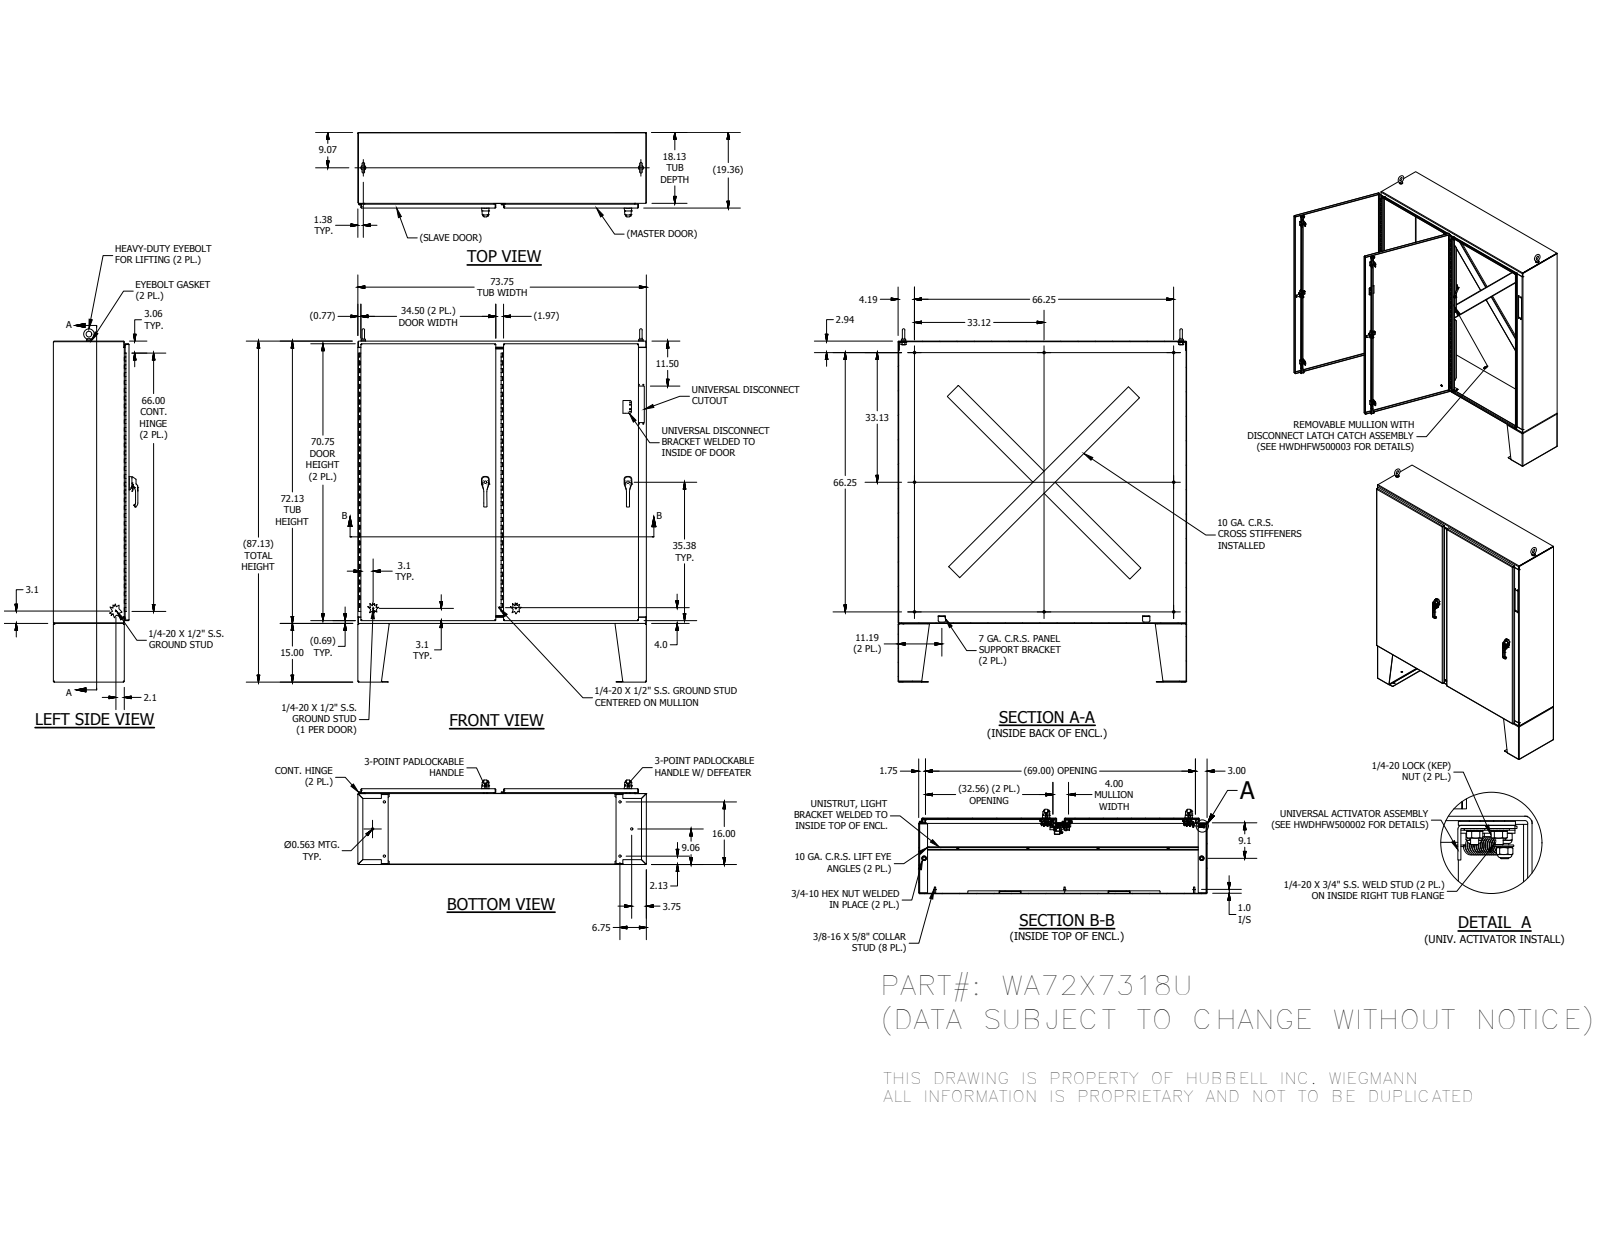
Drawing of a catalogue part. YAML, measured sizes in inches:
part_name: "WA72X7318UBLS; WAX7318UTOP; WAX7318UBTM; HFW332010S (+8 more)"
step_written_by: "Autodesk Inventor 2016 (AUTOMOTIVE_DESIGN)"
units: inches
bodies: {solids: 216, faces: 8897, planar: 4142, cylindrical: 2994, other: 1761}
overall_size: [90.248, 73.75, 21.608]
volume: 2680
surface_area: 41510
round_holes:
  - {diameter: 0.25, count: 18}
  - {diameter: 0.375, count: 18}
  - {diameter: 0.563, count: 18}
  - {diameter: 0.19, count: 8}
  - {diameter: 0.2, count: 8}
  - {diameter: 0.203, count: 8}
  - {diameter: 0.276, count: 8}
  - {diameter: 0.289, count: 8}
  - {diameter: 0.313, count: 8}
  - {diameter: 0.335, count: 8}
  - {diameter: 0.38, count: 8}
  - {diameter: 0.201, count: 7}
round_bosses_or_shafts:
  - {diameter: 0.25, count: 22}
  - {diameter: 0.33, count: 18}
  - {diameter: 0.625, count: 13}
  - {diameter: 0.337, count: 12}
  - {diameter: 0.375, count: 11}
  - {diameter: 0.563, count: 9}
  - {diameter: 1, count: 8}
  - {diameter: 0.438, count: 8}
partial_cylinders:
  - {radius: 0.02, count: 335}
  - {radius: 0.012, count: 203}
  - {radius: 0.02, count: 192}
  - {radius: 0.019, count: 42}
  - {radius: 0.094, count: 41}
  - {radius: 0.05, count: 40}
  - {radius: 0.125, count: 37}
  - {radius: 0.079, count: 27}
face_to_face_distances: [0.134, 19.217, 0.134, 19.083, 19.35, 71.991, 73.75, 73.616, 71.857, 73.482]
hole_center_spacings: [36.5, 0.037, 2, 36.511, 0.036, 0.886, 1.102, 1.142]
